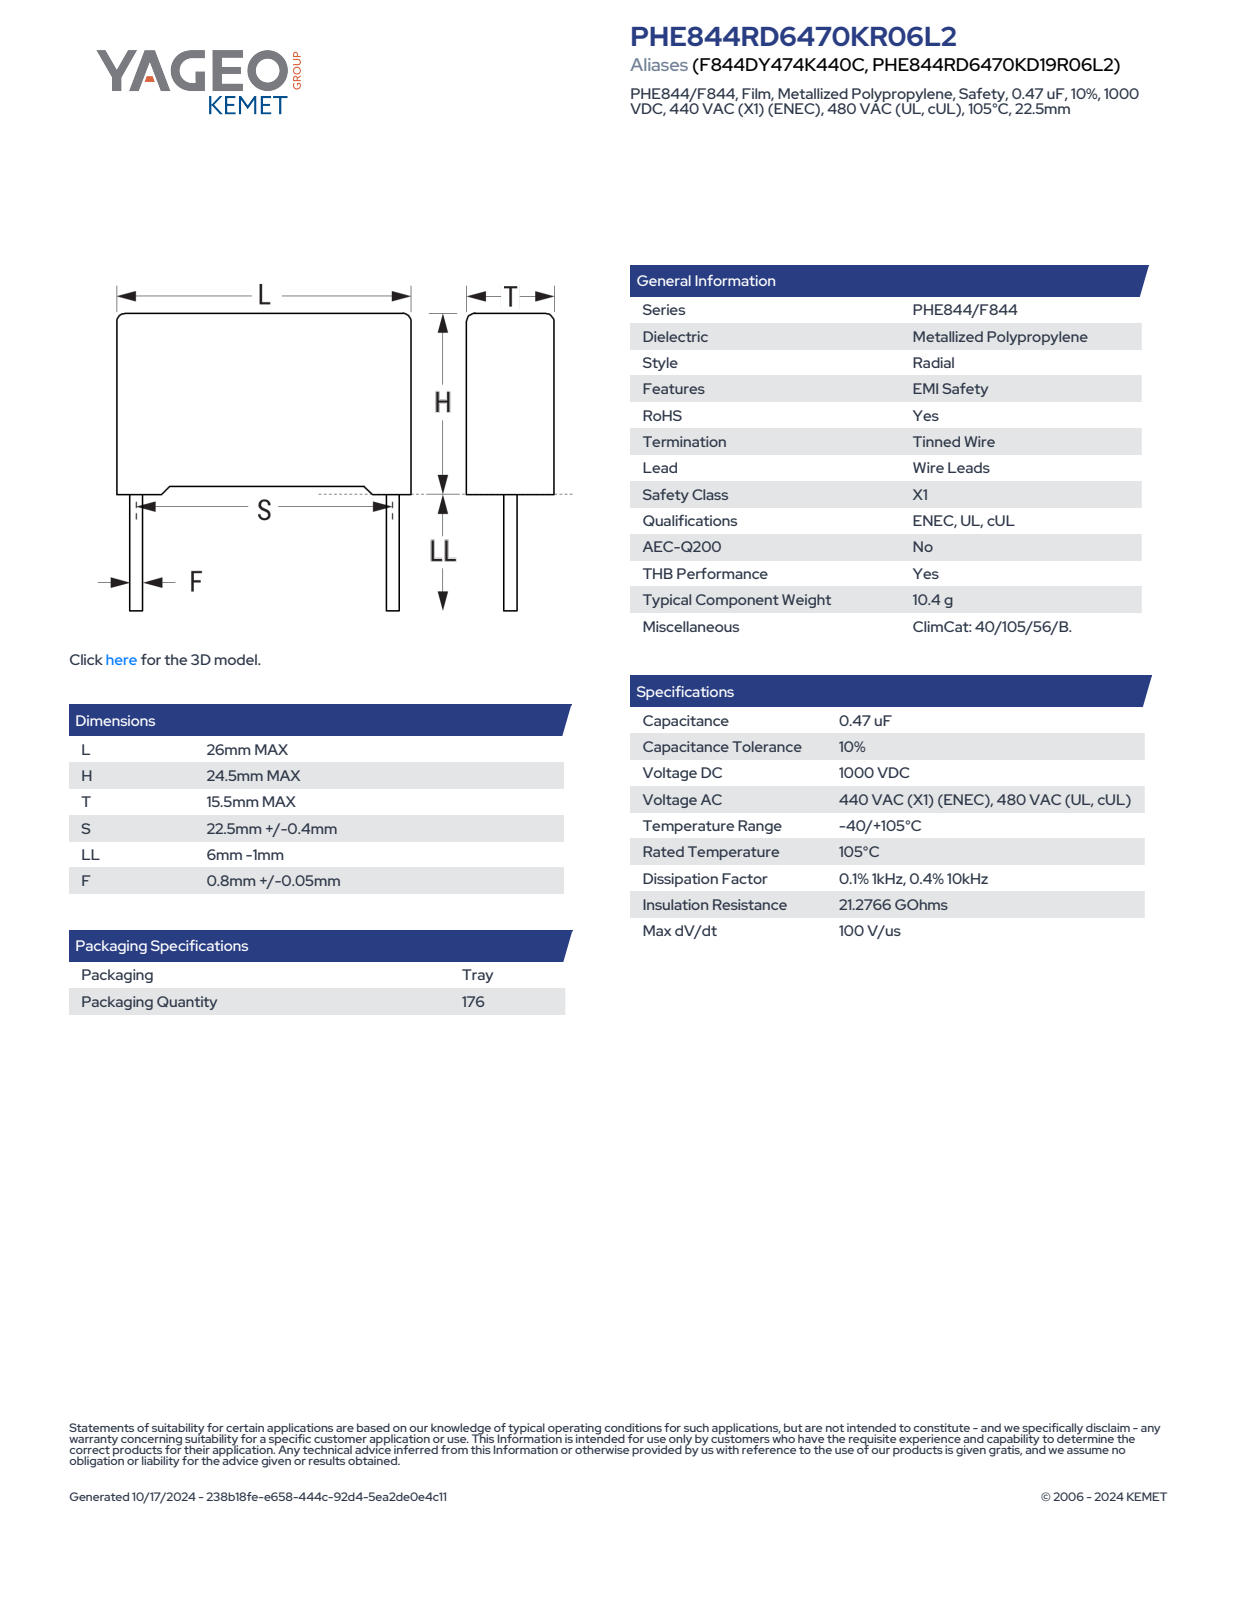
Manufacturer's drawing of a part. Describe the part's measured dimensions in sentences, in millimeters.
The part is named "CFR_RB2_26X24.5X15.5_L26H24.5T15.5S22.5LL5F0.85". Its 3-D file was written by "SolidWorks 2021 (AUTOMOTIVE_DESIGN)". It is 4 solids with 85 faces: 77 planar, 8 cylindrical and 0 other. Overall it measures 29.5 by 26 by 15.51 millimeters. Its volume is 9 574 cubic millimeters and its surface area 2 903 square millimeters. Round bosses or shafts: 2 of diameter 0.85. Partial cylindrical surfaces (rounded edges, fillets, slot ends): 4 of radius 0.5. The main face-to-face distances are 15.5, 26, 23.66, 23.75, 0.75, 0.84, 24.5, 0.87, 25.13, 24.26.
